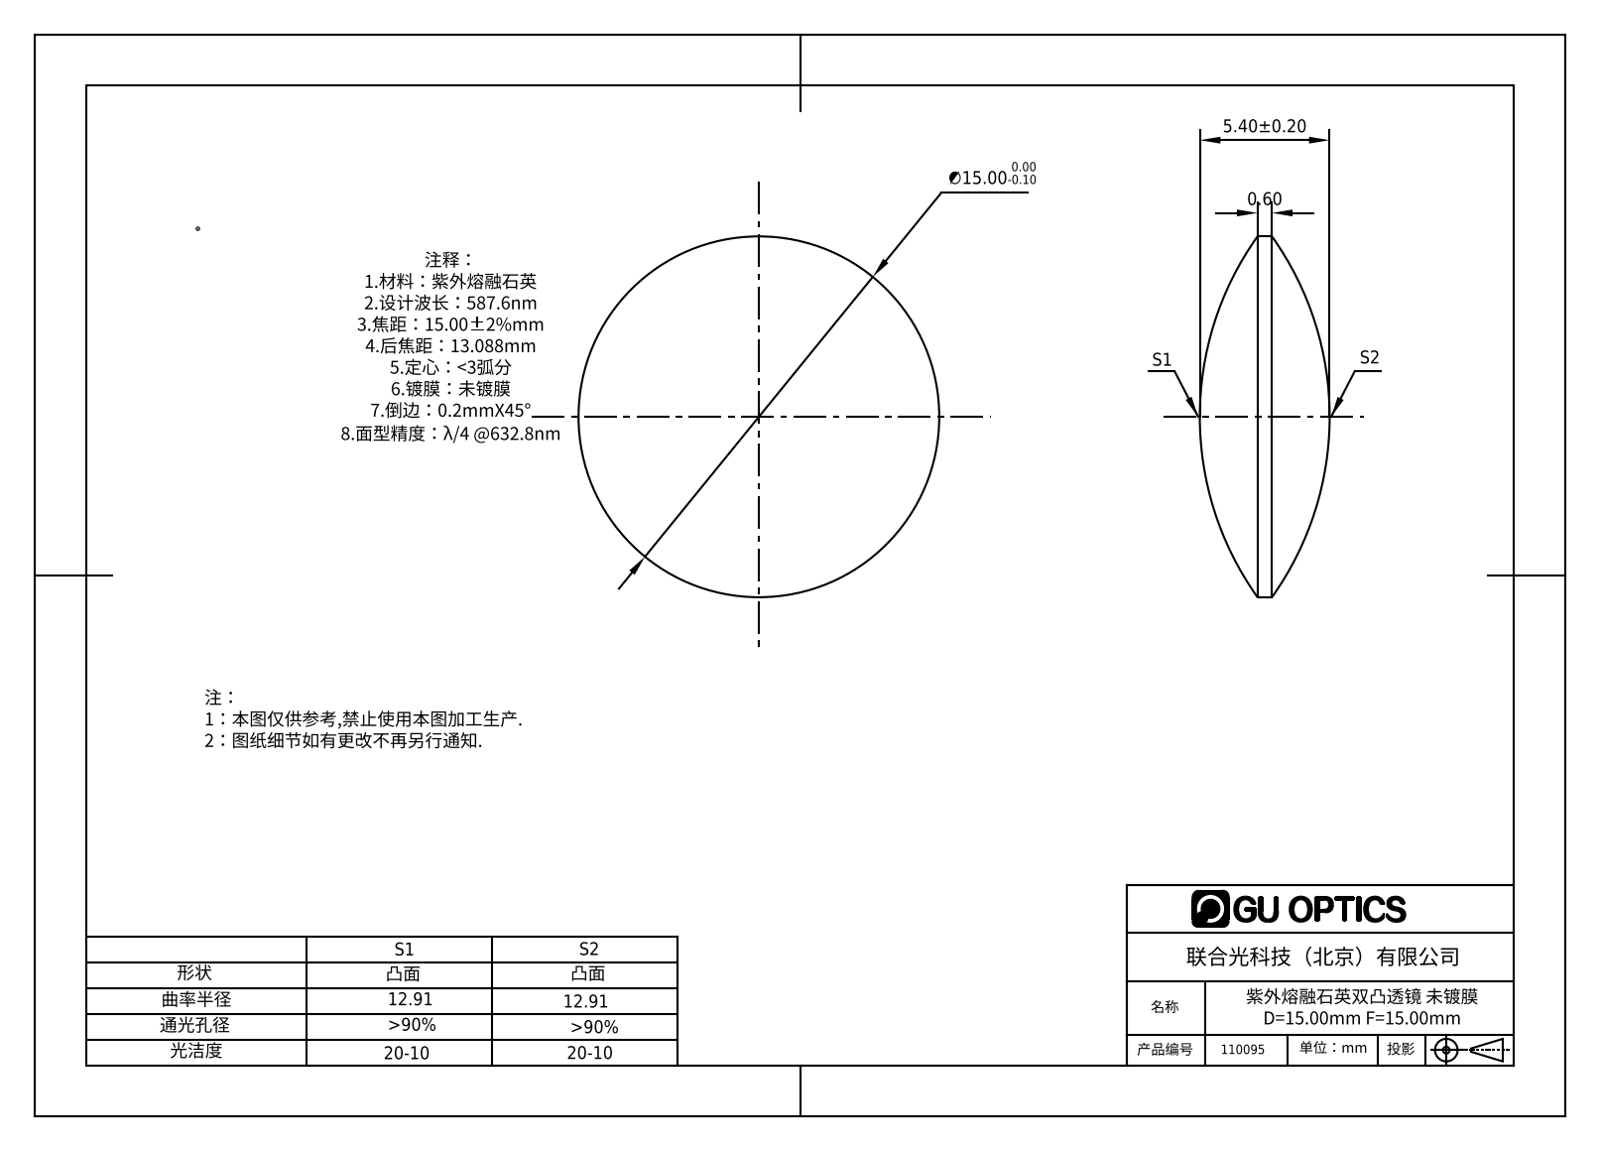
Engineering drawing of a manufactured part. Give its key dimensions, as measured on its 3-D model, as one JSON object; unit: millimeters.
{"part_name": "110095", "step_written_by": "SolidWorks 2016 (CONFIG_CONTROL_DESIGN)", "units": "millimeters", "bodies": {"solids": 1, "faces": 6, "planar": 0, "cylindrical": 2, "other": 4}, "overall_size": [15, 15, 5.4], "volume_mm3": 545, "surface_area_mm2": 418, "round_bosses_or_shafts": [[15, 1]]}
